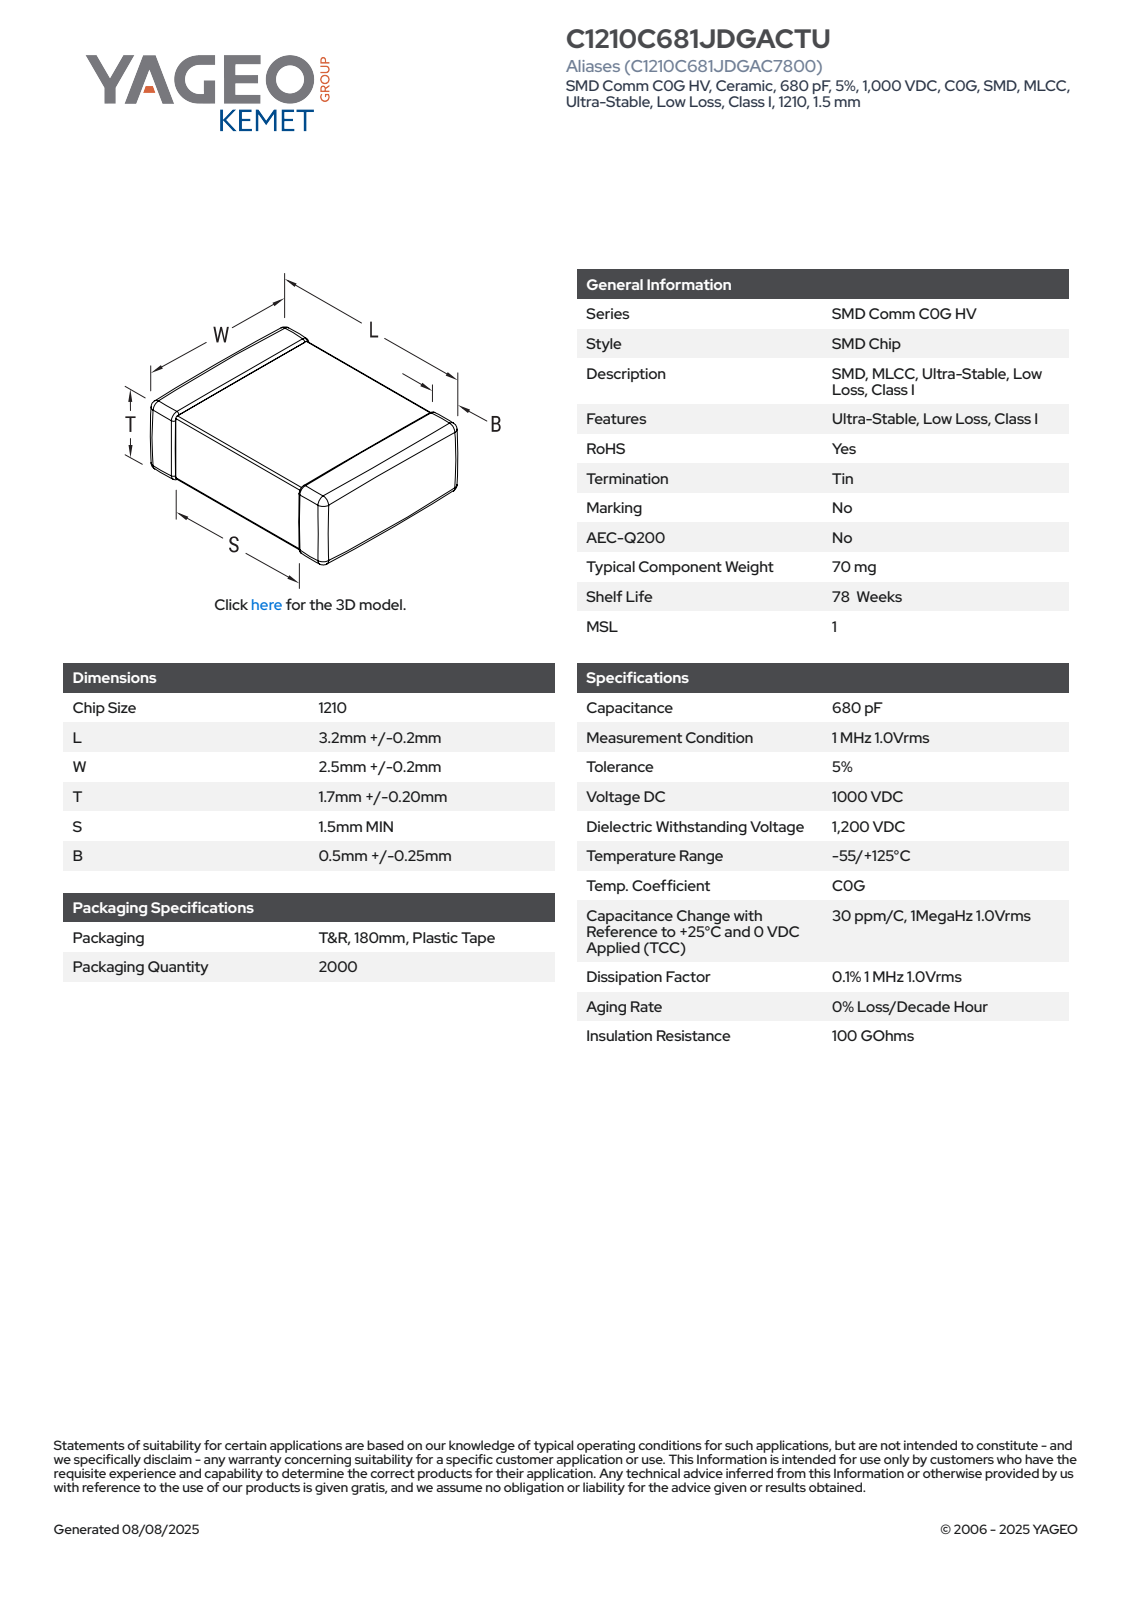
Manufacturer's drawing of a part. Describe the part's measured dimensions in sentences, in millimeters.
The part is named "CCS_CCSTDNOS_1210_L3.4W2.7T1.9B0.75". Its 3-D file was written by "SolidWorks 2014 (AUTOMOTIVE_DESIGN)". It is 4 solids with 125 faces: 71 planar, 38 cylindrical and 16 other. Overall it measures 3.4 by 2.7 by 1.9 millimeters. Its volume is 16 cubic millimeters and its surface area 41 square millimeters. The main face-to-face distances are 1.84, 1.78, 3.4, 2.64, 1.9, 2.58, 2.7, 1.85, 1.79, 1.31.
